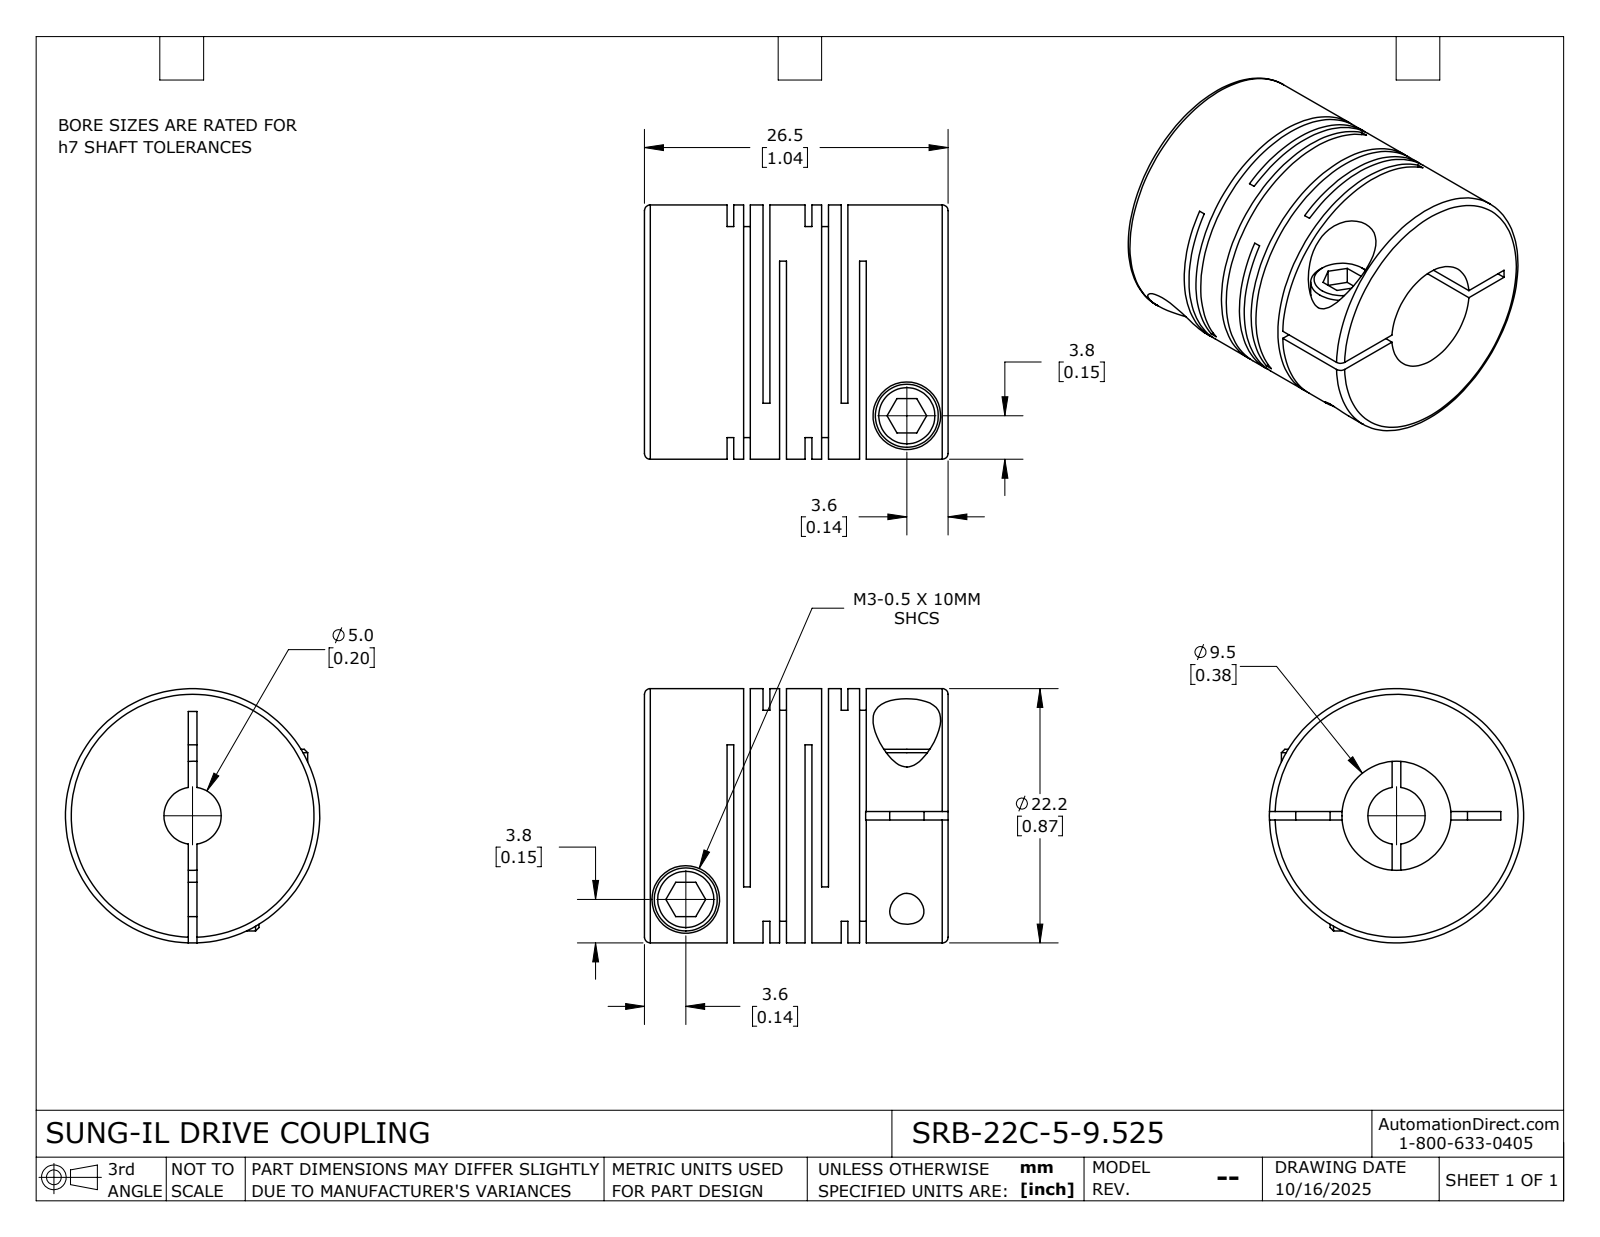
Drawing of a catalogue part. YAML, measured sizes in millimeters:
part_name: "SRB-22C-5-9.525"
step_written_by: "SolidWorks 2024 (CONFIG_CONTROL_DESIGN)"
units: millimeters
bodies: {solids: 1, faces: 115, planar: 60, cylindrical: 42, other: 13}
overall_size: [26.5, 22.2, 22.2]
volume: 7222
surface_area: 7588
round_holes:
  - {diameter: 3, count: 2}
  - {diameter: 5.9, count: 2}
  - {diameter: 5, count: 1}
  - {diameter: 9.53, count: 1}
round_bosses_or_shafts:
  - {diameter: 5.5, count: 2}
  - {diameter: 22.2, count: 1}
face_to_face_distances: [0.59, 6.82, 1.45, 3.15, 5.37, 3.67, 1.7, 7.41, 6.23, 2.04]
